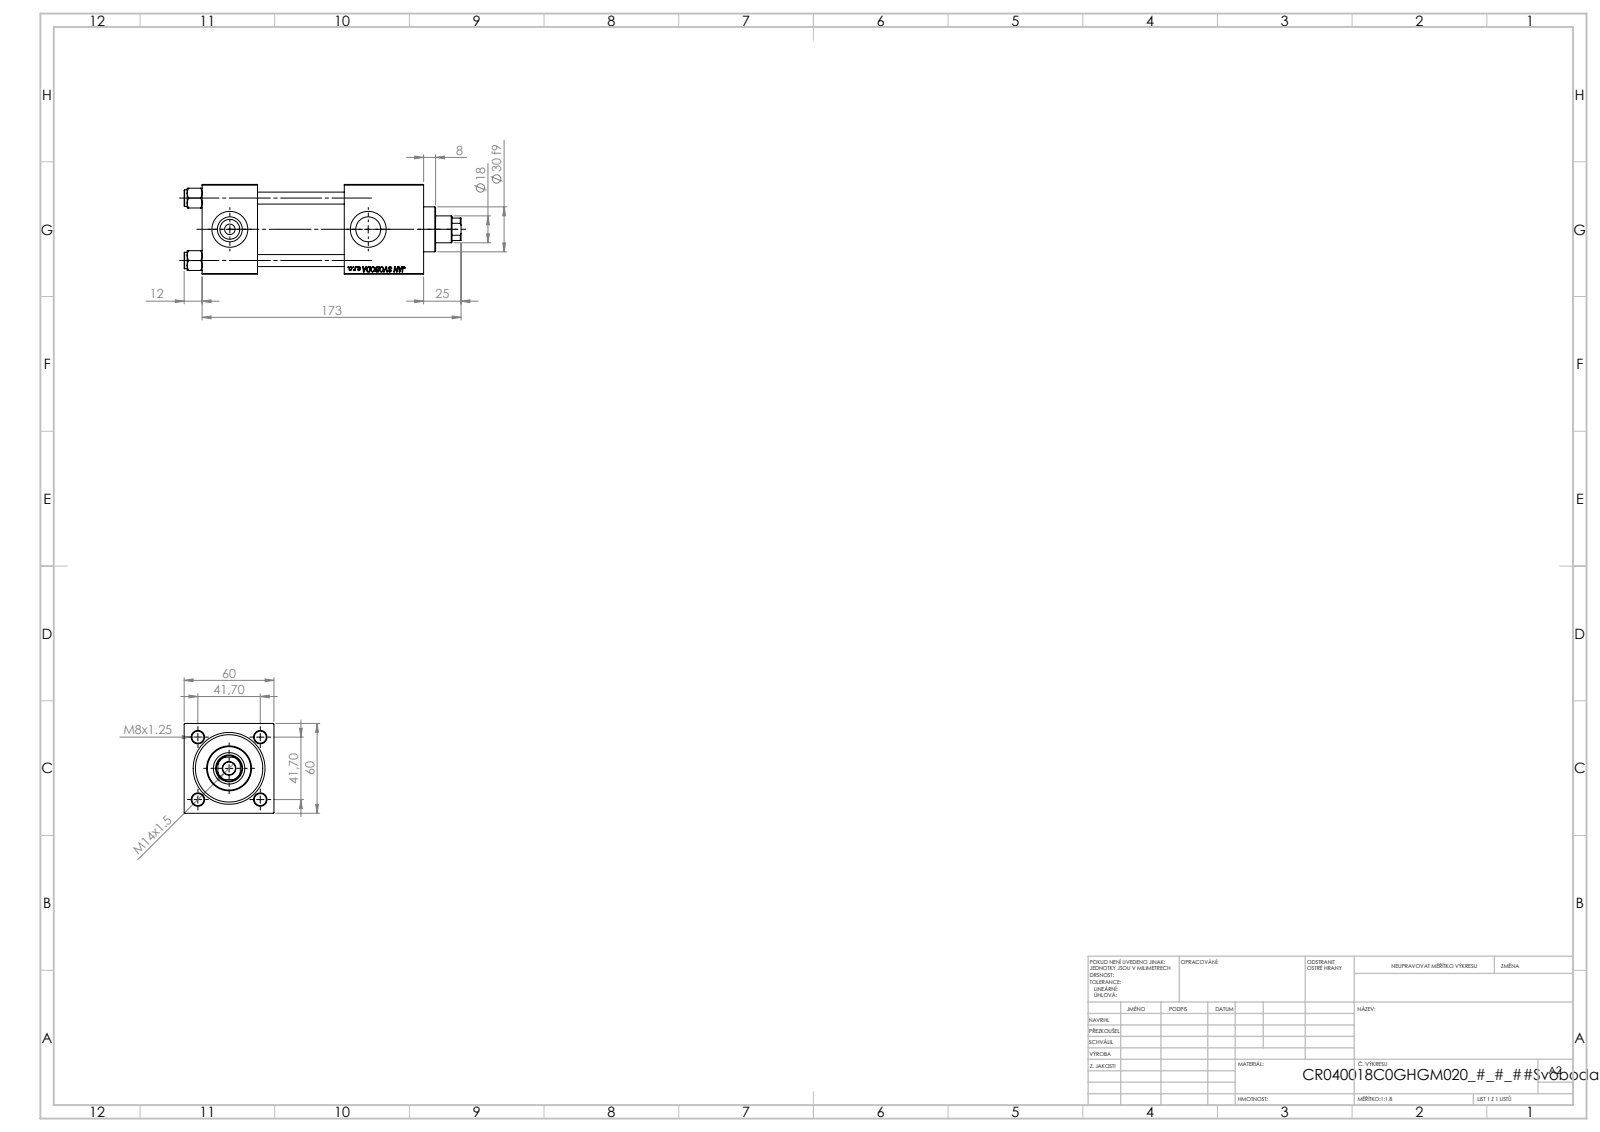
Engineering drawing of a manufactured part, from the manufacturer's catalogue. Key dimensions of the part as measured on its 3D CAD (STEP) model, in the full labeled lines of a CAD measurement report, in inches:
Part name (STEP PRODUCT): V215_VC_A; V215CR_VCP_C; NUT_M5_C; V215CR_C_TYCINKA (+1 more)
STEP written by: SolidWorks 2019 (CONFIG_CONTROL_DESIGN)
Units: inches
Bodies: 11 solids, 1148 faces (526 planar, 86 cylindrical, 536 other)
Overall size (bounding box): 7.283 × 2.362 × 2.362
Volume: 24.57 in³ · Surface area: 163.3 in²
Round holes (diameter × count): ⌀0.315 ×4, ⌀0.276 ×2, ⌀0.656 ×2, ⌀0.945 ×2, ⌀0.335 ×1, ⌀0.709 ×1, ⌀0.827 ×1, ⌀1.22 ×1, ⌀1.575 ×1, ⌀1.772 ×1
Round bosses / shafts (diameter × count): ⌀0.433 ×4, ⌀1.811 ×1, ⌀1.181 ×1
Partial cylindrical surfaces — rounded edges, fillets, slot ends (radius × count): R0.335 ×1
Main face-to-face distances: 2.362, 1.457, 2.087, 5.827, 4.37, 2.283, 3.74, 4.697, 3.24, 0.957
Hole centre spacings: 1.161, 1.642, 2.322, 3.642
